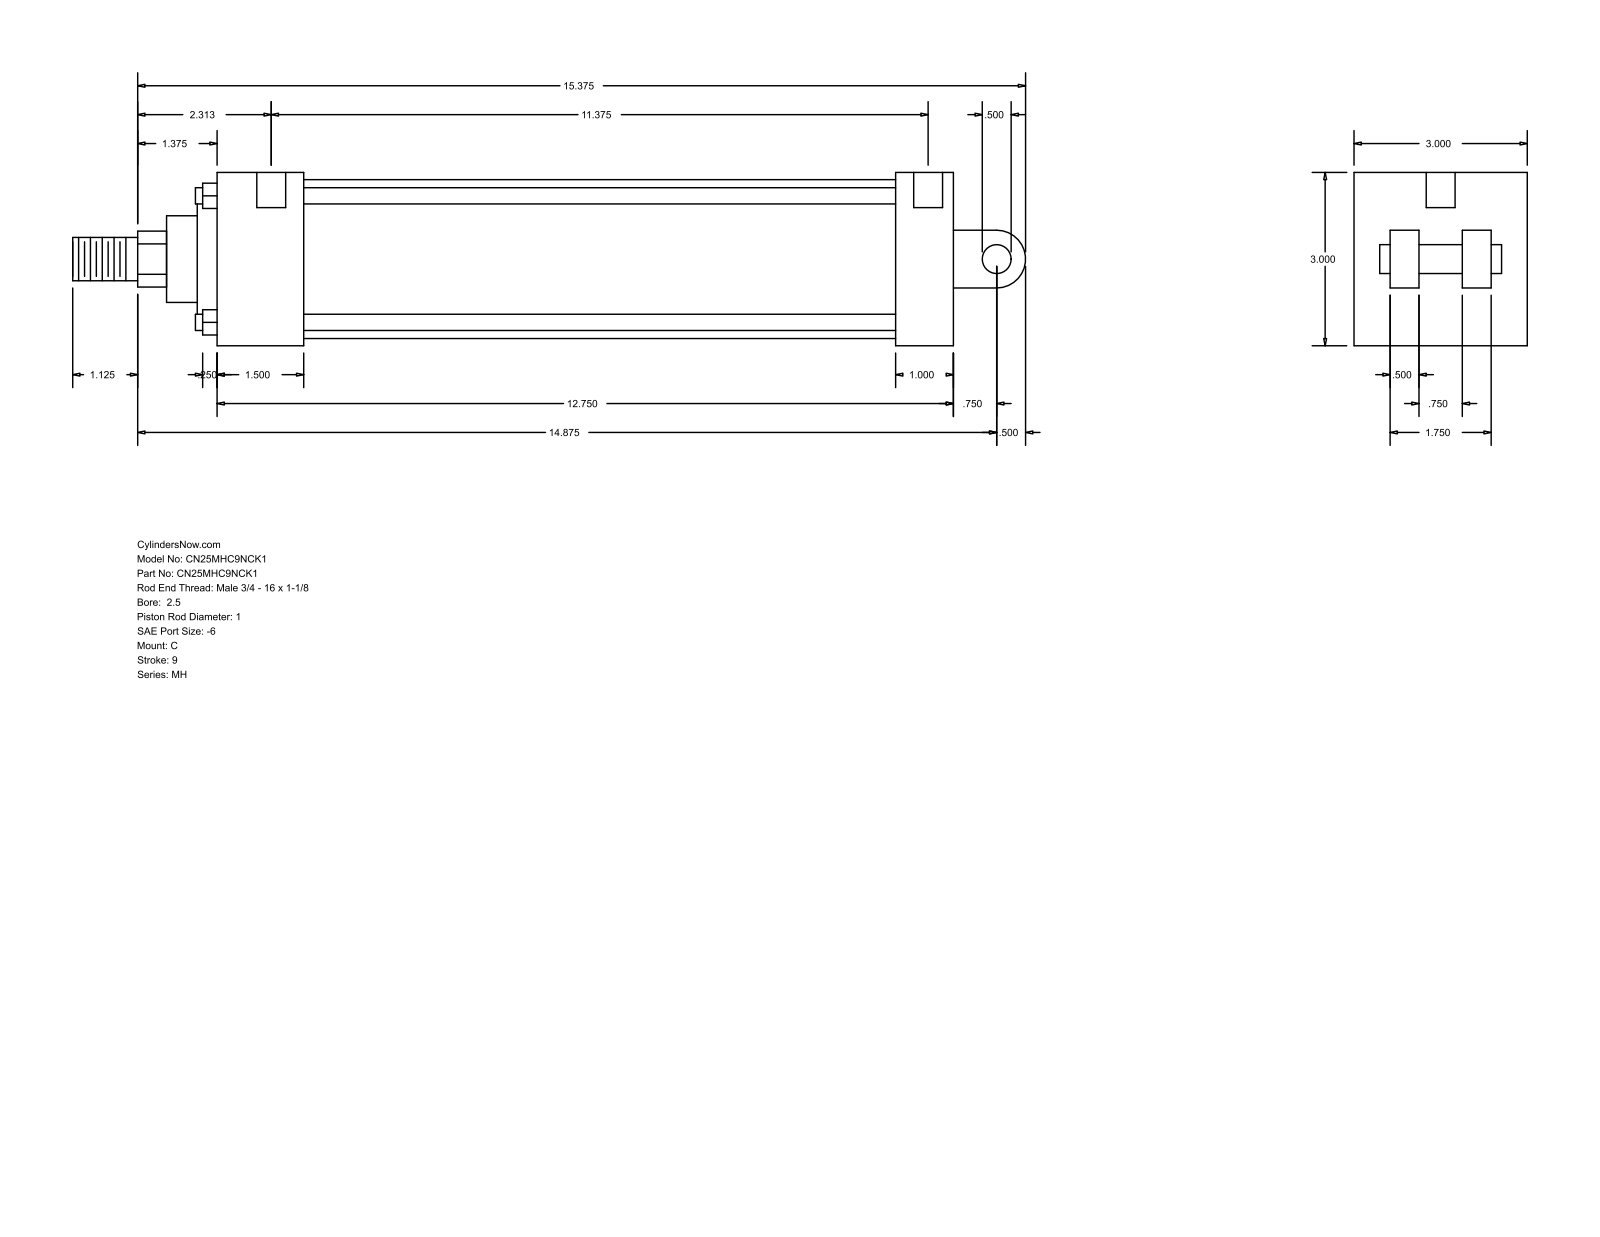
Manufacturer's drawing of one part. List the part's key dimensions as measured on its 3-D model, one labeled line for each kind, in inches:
Part name (STEP PRODUCT): MH_C__0250_1
STEP written by: GSSL Pune (CONFIG_CONTROL_DESIGN)
Units: inches
Bodies: 0 solids, 101 faces (71 planar, 30 cylindrical, 0 other)
Overall size (bounding box): 16.5 × 3 × 3
Round holes (diameter × count): ⌀0.219 ×4, ⌀0.5 ×2
Round bosses / shafts (diameter × count): ⌀0.281 ×4, ⌀2.75 ×1, ⌀2.375 ×1, ⌀1.5 ×1, ⌀1 ×1, ⌀0.75 ×1, ⌀0.5 ×1
Partial cylindrical surfaces — rounded edges, fillets, slot ends (radius × count): R0.484 ×1, R0.5 ×1
Main face-to-face distances: 3, 12.75, 1, 2.375, 0.625, 11.75, 1.5, 10.25, 11.25, 0.5
Hole centre spacings: 11.687, 0.125, 0.187, 11.375, 11.5, 11.562
